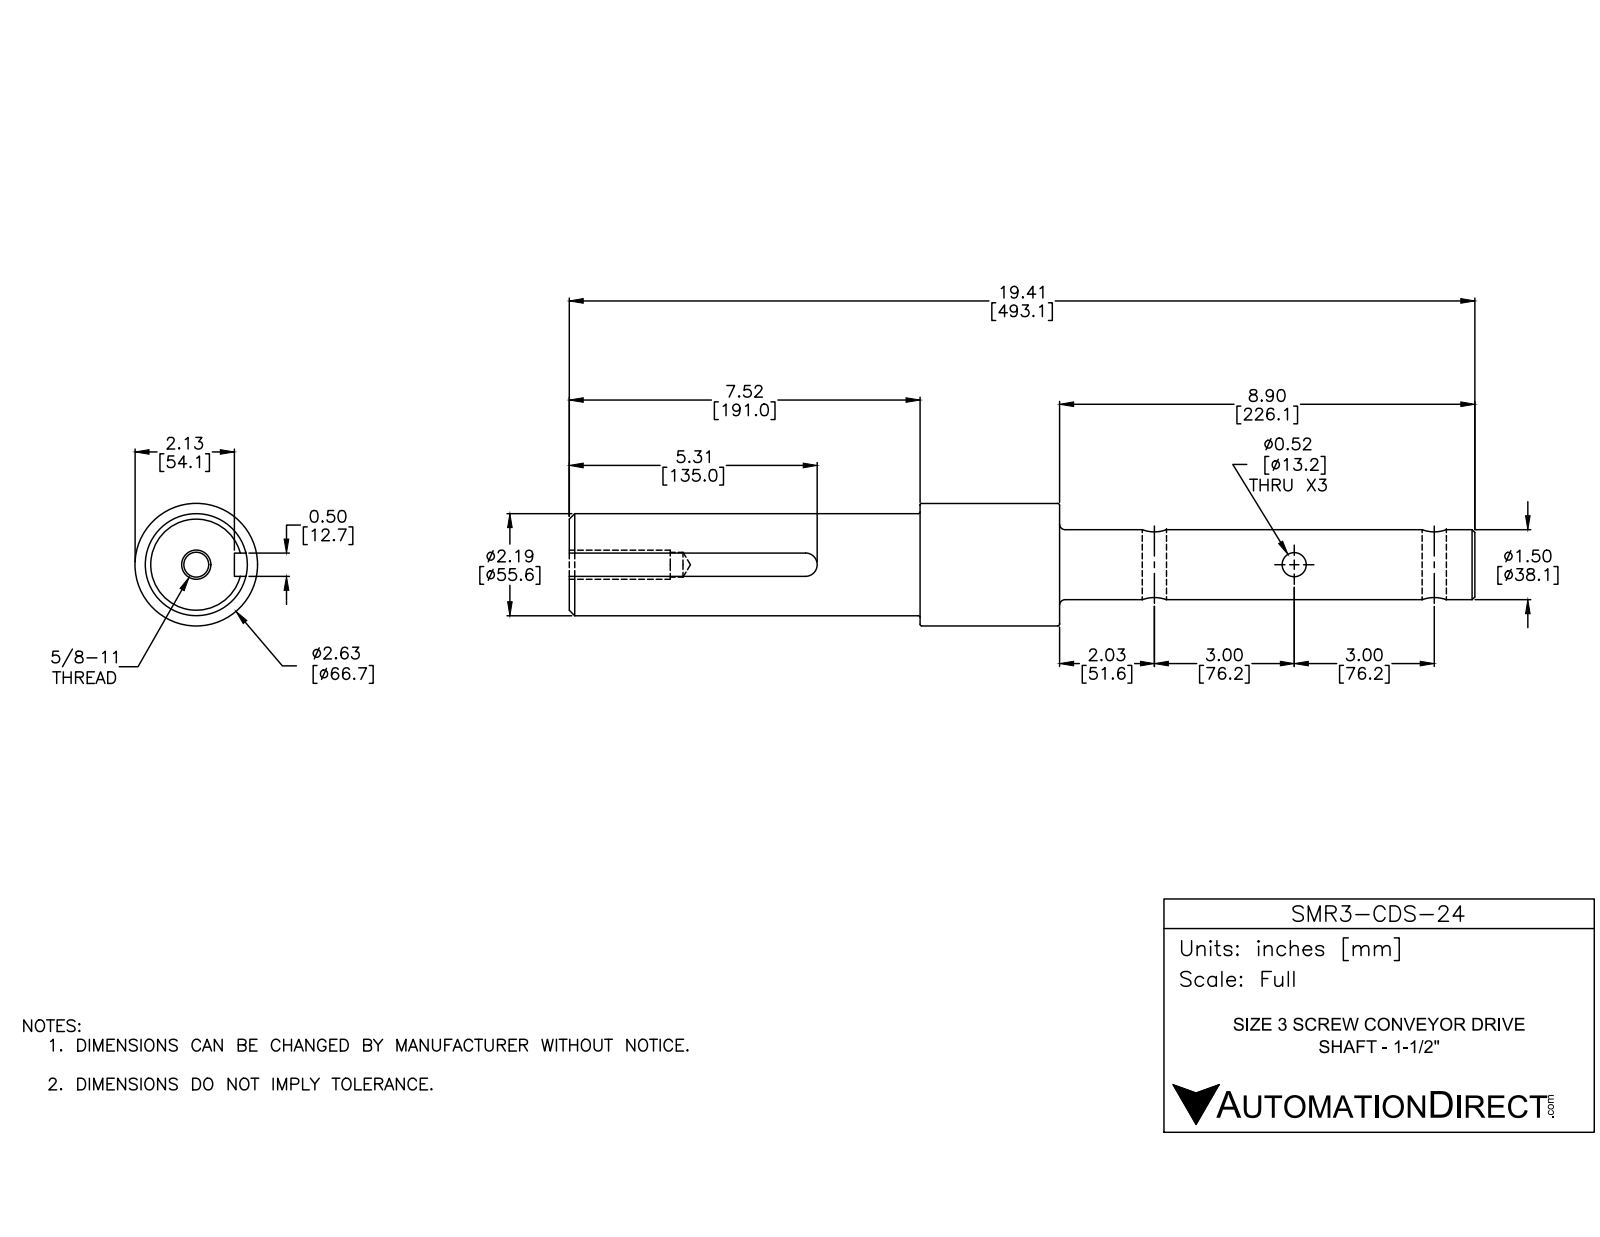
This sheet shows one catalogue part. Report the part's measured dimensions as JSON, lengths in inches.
{"part_name": "SMR3-CDS-24", "step_written_by": "SolidWorks 2016 (AUTOMOTIVE_DESIGN)", "units": "inches", "bodies": {"solids": 1, "faces": 40, "planar": 8, "cylindrical": 18, "other": 14}, "overall_size": [19.413, 2.625, 2.625], "volume_in3": 57.76, "surface_area_in2": 141, "round_holes": [[0.52, 3], [0.531, 1], [0.625, 1]], "round_bosses_or_shafts": [[2.625, 1], [2.187, 1], [1.5, 1]], "partial_cylinders_radius": [[0.25, 1]], "face_to_face_distances": [10.512, 19.413, 8.902, 0.5, 7.52, 2.992, 11.894, 2.165, 5.354, 8.346], "hole_center_spacings": [6]}
